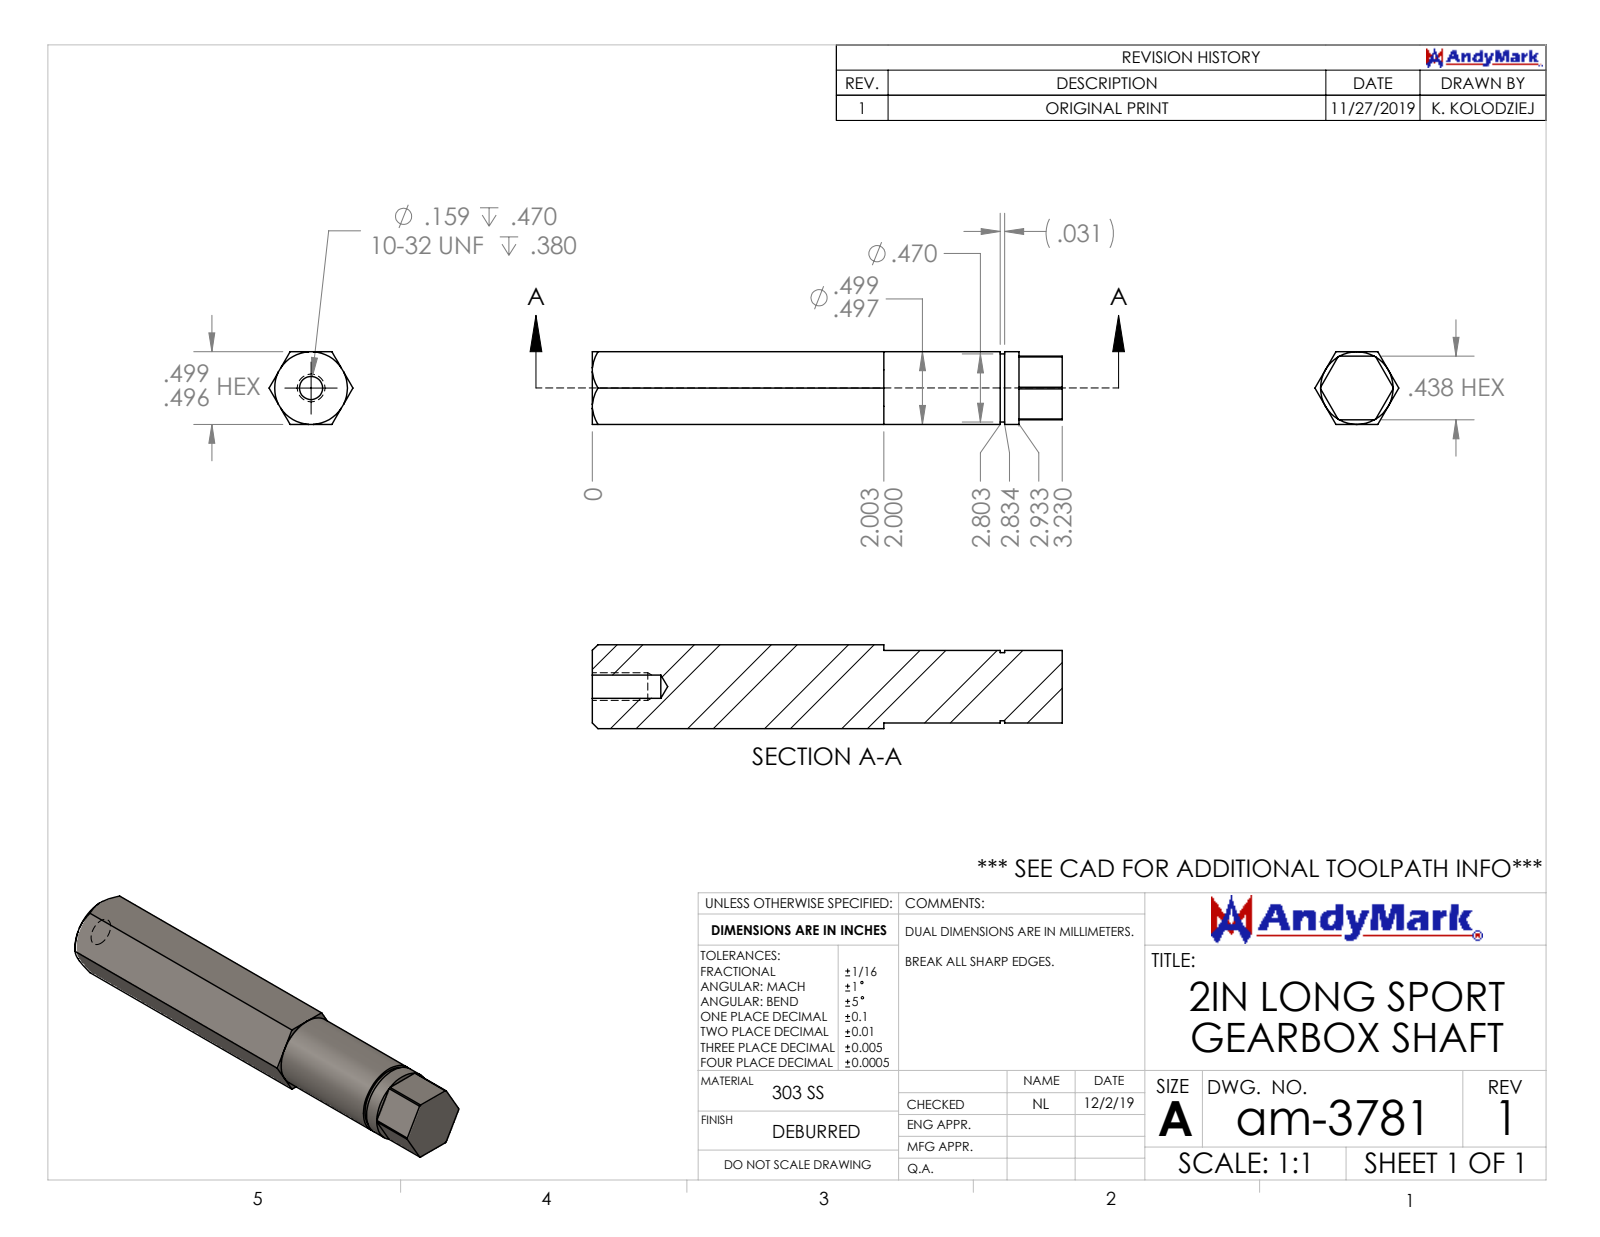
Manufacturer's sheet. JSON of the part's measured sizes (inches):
{"part_name": "am-3781 2IN Long Sport Gearbox Shaft", "step_written_by": "SolidWorks 2019 (AUTOMOTIVE_DESIGN)", "units": "inches", "bodies": {"solids": 1, "faces": 44, "planar": 28, "cylindrical": 8, "other": 8}, "overall_size": [3.23, 0.576, 0.499], "volume_in3": 0.652, "surface_area_in2": 6.067, "round_holes": [[0.159, 1]], "round_bosses_or_shafts": [[0.499, 1], [0.468, 1]], "face_to_face_distances": [0.499, 0.031, 0.469, 0.438, 3.23, 0.297, 2.933, 0.396, 0.099, 2.834]}
